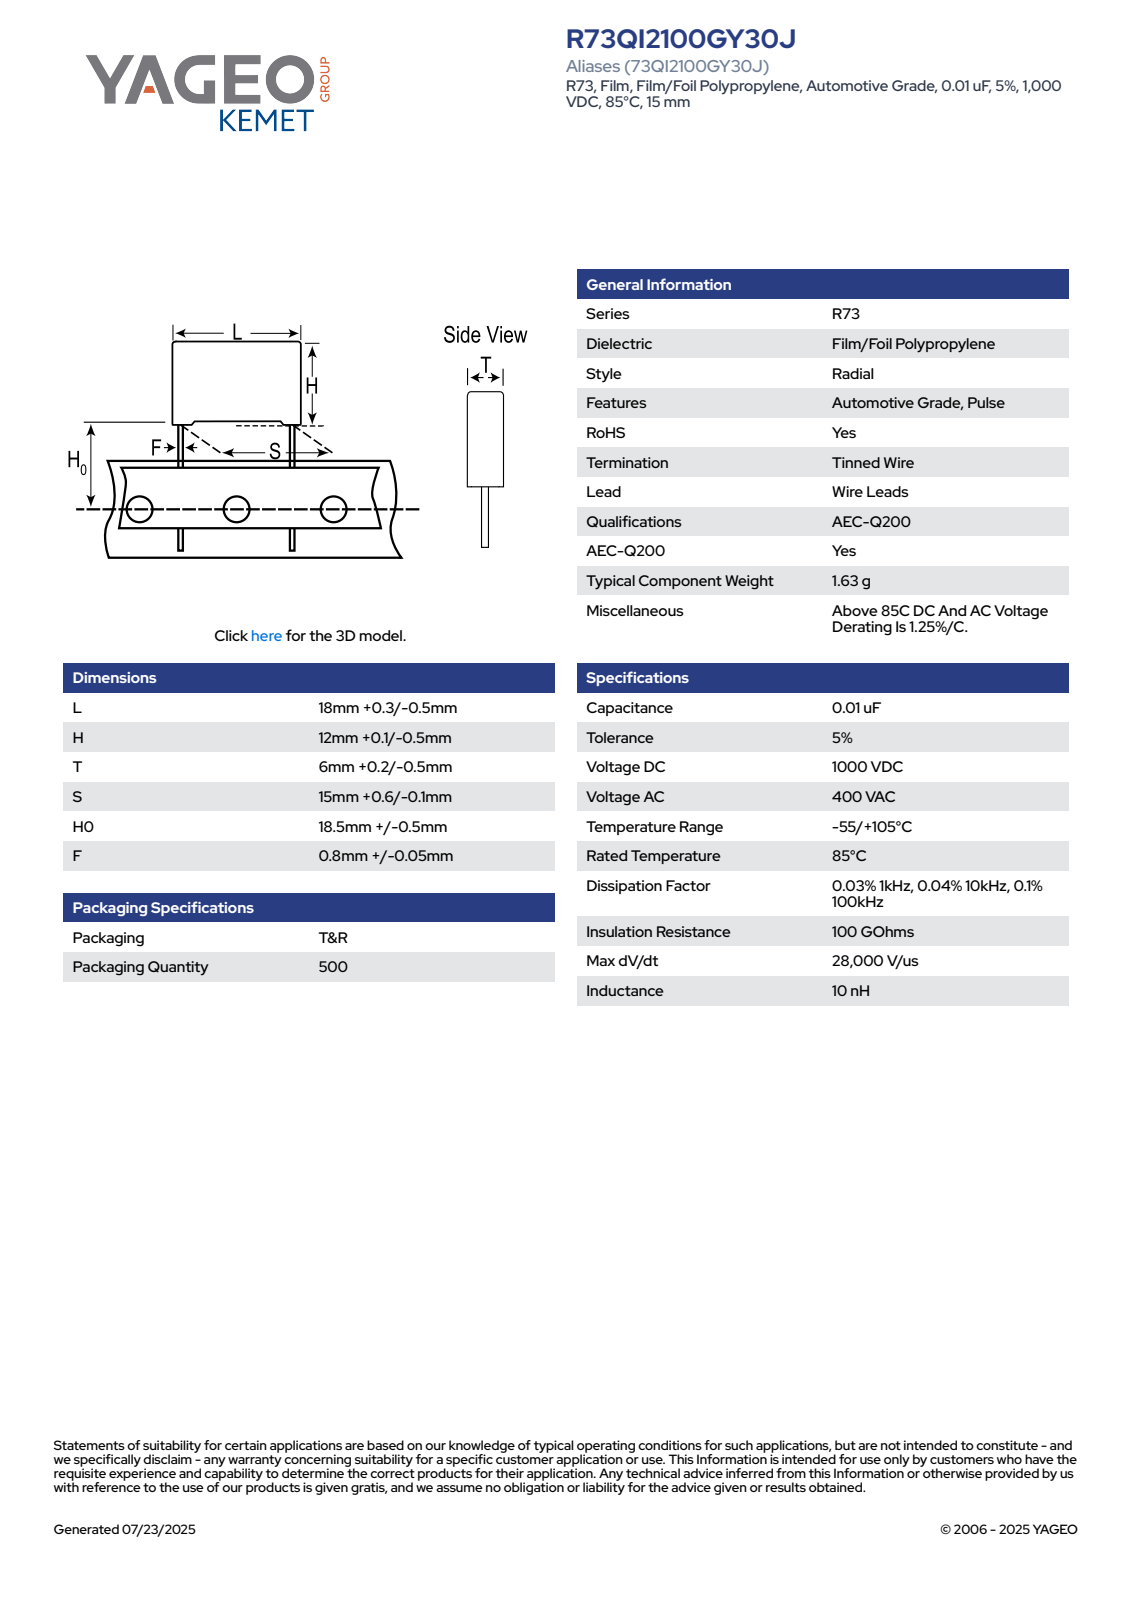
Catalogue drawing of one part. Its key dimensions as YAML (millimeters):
part_name: "CFR_RB2_18X12X6_L18.3H12.1T6.2S15H019F0.85"
step_written_by: "SolidWorks 2020 (AUTOMOTIVE_DESIGN)"
units: millimeters
bodies: {solids: 4, faces: 85, planar: 77, cylindrical: 8, other: 0}
overall_size: [31.1, 18.3, 6.21]
volume: 1323
surface_area: 954
round_bosses_or_shafts:
  - {diameter: 0.85, count: 2}
partial_cylinders:
  - {radius: 0.5, count: 4}
face_to_face_distances: [6.2, 11.35, 18.3, 0.61, 5.59, 0.75, 12.1, 0.42, 0.33, 11.68]
